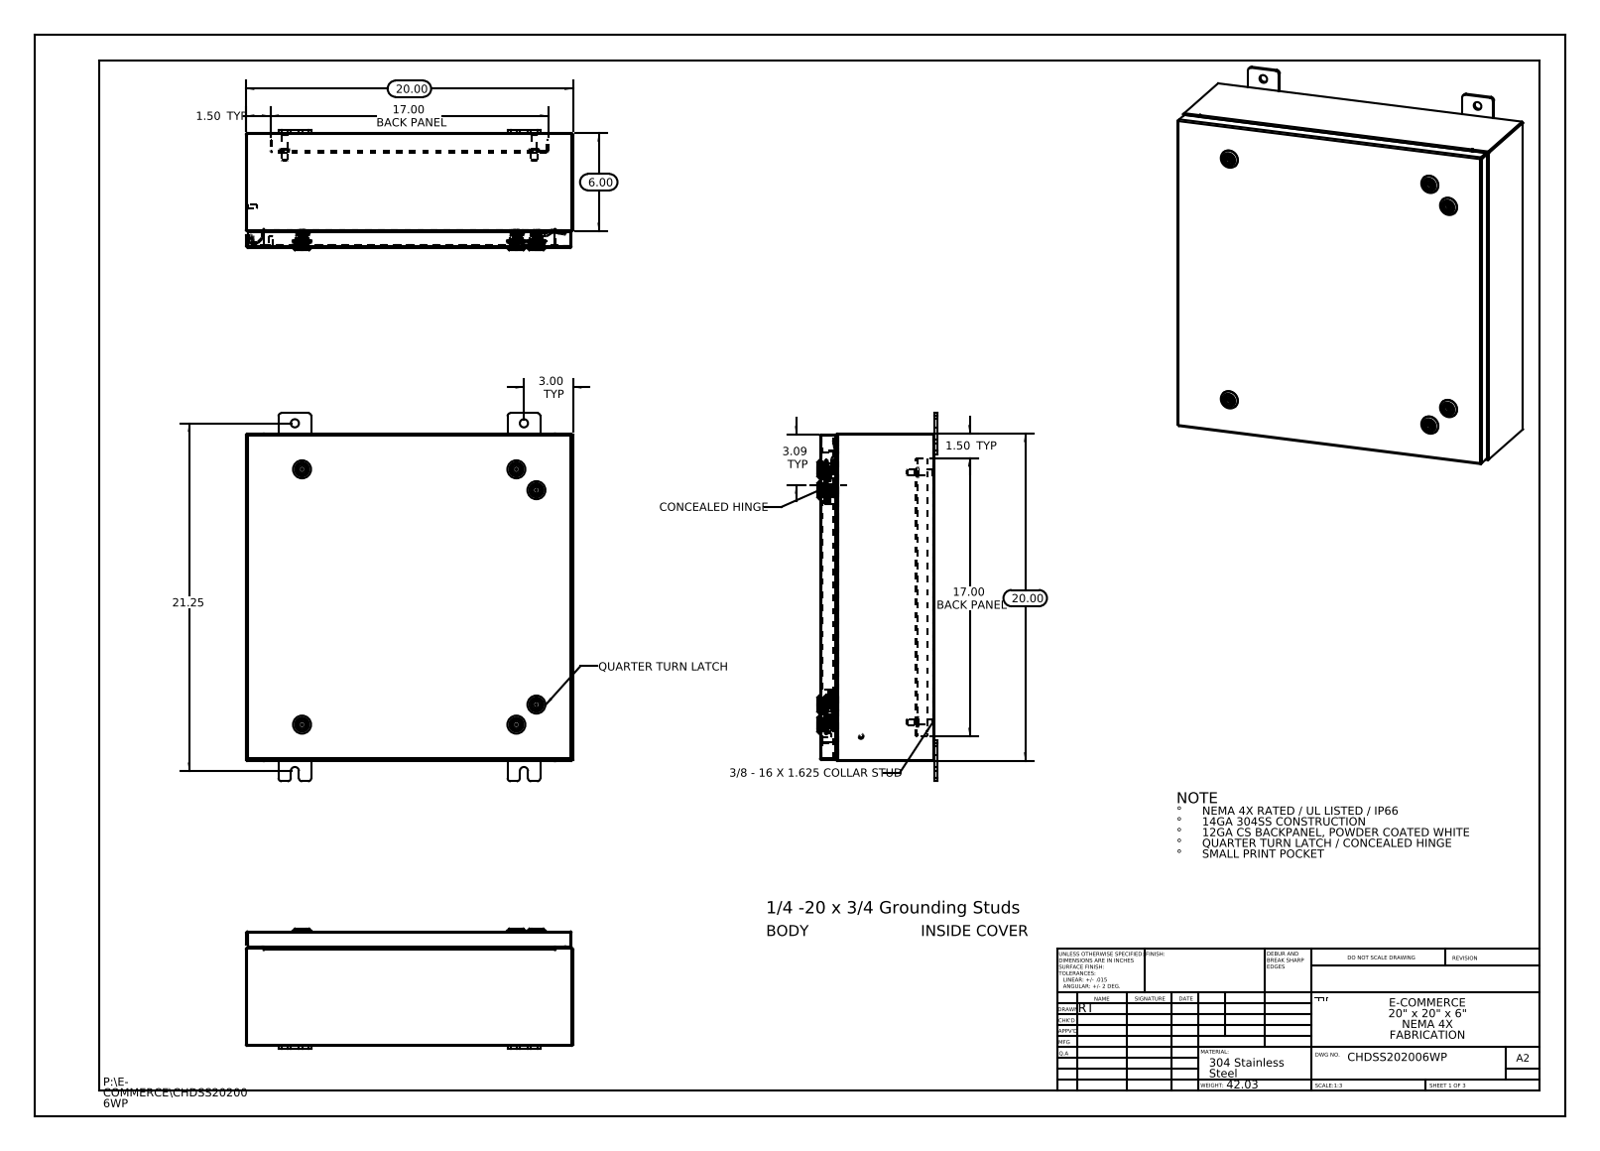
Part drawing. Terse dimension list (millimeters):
name: HW-CLH-E5-8004_Cam-232112-U-Industrilas; CHDSS202006WP Backpanel; CHDSS202006WP Mounting Studs; CHDSS202006WP Top (+8 more)
written by: SolidWorks 2013 (CONFIG_CONTROL_DESIGN)
unit: mm
bodies: 55 solids, 5420 faces (1592 planar, 1692 cylindrical, 2136 other)
size: 1148.4 × 571.5 × 186.8
volume: 2 481 000 mm³; area: 2 432 000 mm²
holes: 8× ⌀12.7, 6× ⌀5, 6× ⌀10, 6× ⌀10.2, 6× ⌀16, 6× ⌀20, 4× ⌀3.5, 2× ⌀5.4
bosses: 8× ⌀6, 6× ⌀28, 6× ⌀19.8, 6× ⌀15.9, 6× ⌀15.5, 6× ⌀13.5, 6× ⌀10, 6× ⌀2.9
rounds: 198× R0.2, 198× R3, 72× R0.7, 24× R0.5, 24× R4.8, 24× R5, 20× R0.3, 18× R2.2
face distances: 1.9, 1.9, 506.1, 178.1, 176.1, 176.2, 174.3, 2.6, 25.4, 27.3
hole spacings: 332.7, 47.2, 77.9, 355.6, 365.2, 387.4, 387.4, 396.2
